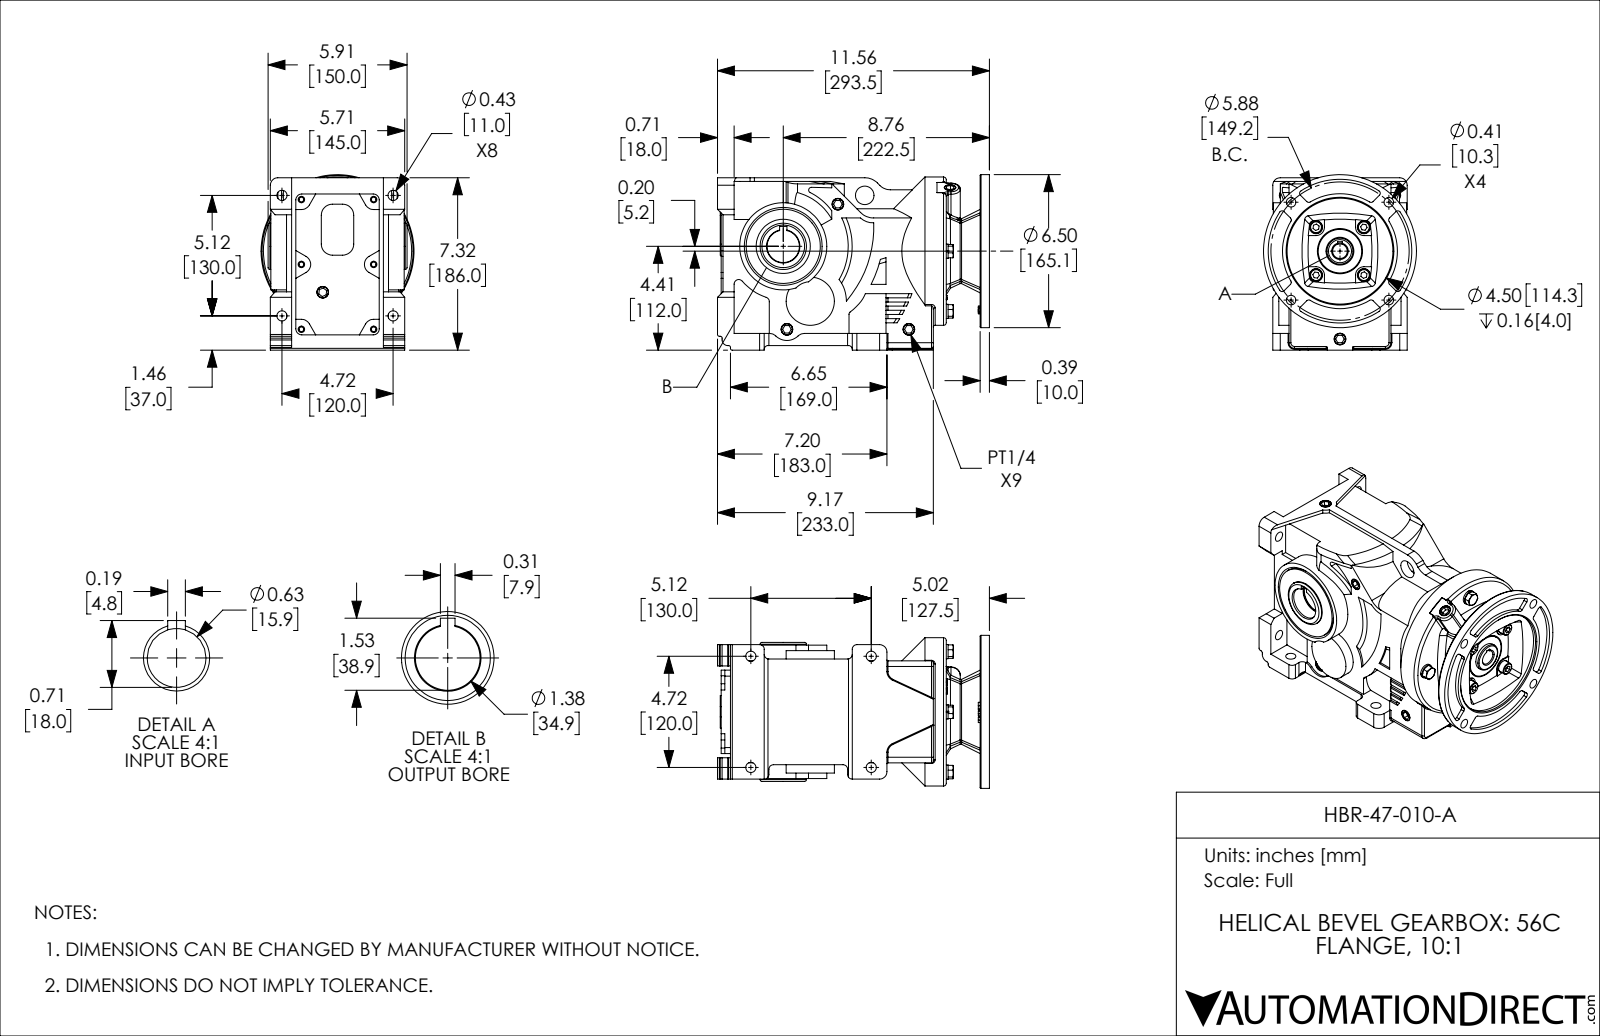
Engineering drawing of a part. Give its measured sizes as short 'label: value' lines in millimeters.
name: HBR-47-010-A
written by: SolidWorks 2018 (AUTOMOTIVE_DESIGN)
unit: mm
bodies: 1 solid, 1002 faces (447 planar, 317 cylindrical, 238 other)
size: 293.5 × 189.4 × 165.1
volume: 5 059 000 mm³; area: 319 500 mm²
holes: 8× ⌀11, 6× ⌀5, 6× ⌀7, 4× ⌀8.2, 4× ⌀9, 4× ⌀10.3, 4× ⌀14, 1× ⌀15.9, 1× ⌀20, 1× ⌀21.5, 1× ⌀34.9, 1× ⌀37
bosses: 4× ⌀15.4, 4× ⌀13, 4× ⌀8, 1× ⌀165.1, 1× ⌀160, 1× ⌀94, 1× ⌀80, 1× ⌀52
rounds: 22× R3, 18× R2, 12× R10, 10× R5, 9× R12, 5× R1, 4× R6.5, 4× R8
face distances: 5, 10, 6, 4, 279.5, 110, 3, 2, 285.5, 275.5
hole spacings: 46.9, 54.2, 83.1, 94.4, 129, 130, 36.5, 38.1
